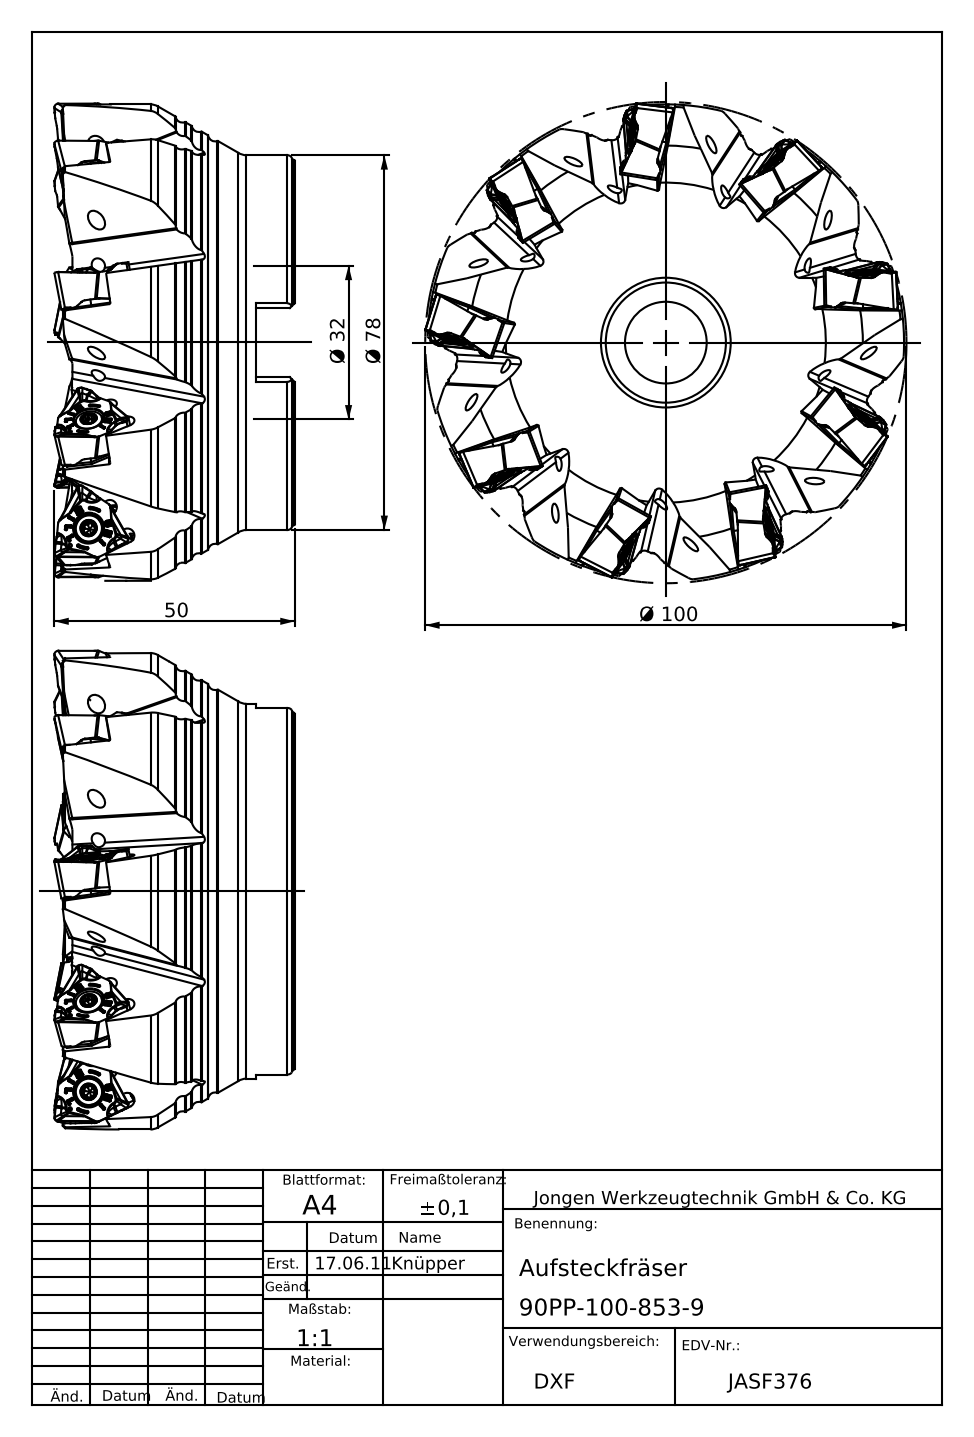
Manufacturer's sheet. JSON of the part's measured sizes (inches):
{"part_name": "90PP-100-853-9", "step_written_by": "SolidWorks 2010 (AUTOMOTIVE_DESIGN)", "units": "inches", "bodies": {"solids": 1, "faces": 622, "planar": 204, "cylindrical": 171, "other": 247}, "overall_size": [3.937, 3.937, 1.969], "volume_in3": 15.55, "surface_area_in2": 63.31, "round_holes": [[0.118, 9], [0.669, 1], [0.984, 1], [1.26, 1], [1.266, 1], [1.272, 1]], "round_bosses_or_shafts": [[3.937, 1], [3.904, 1], [3.071, 1]], "partial_cylinders_radius": [[0.012, 63], [0.059, 18]], "face_to_face_distances": [1.821, 1.898, 0.077, 0.315, 1.506, 1.583, 1.102, 0.787, 0.719, 0.795]}
